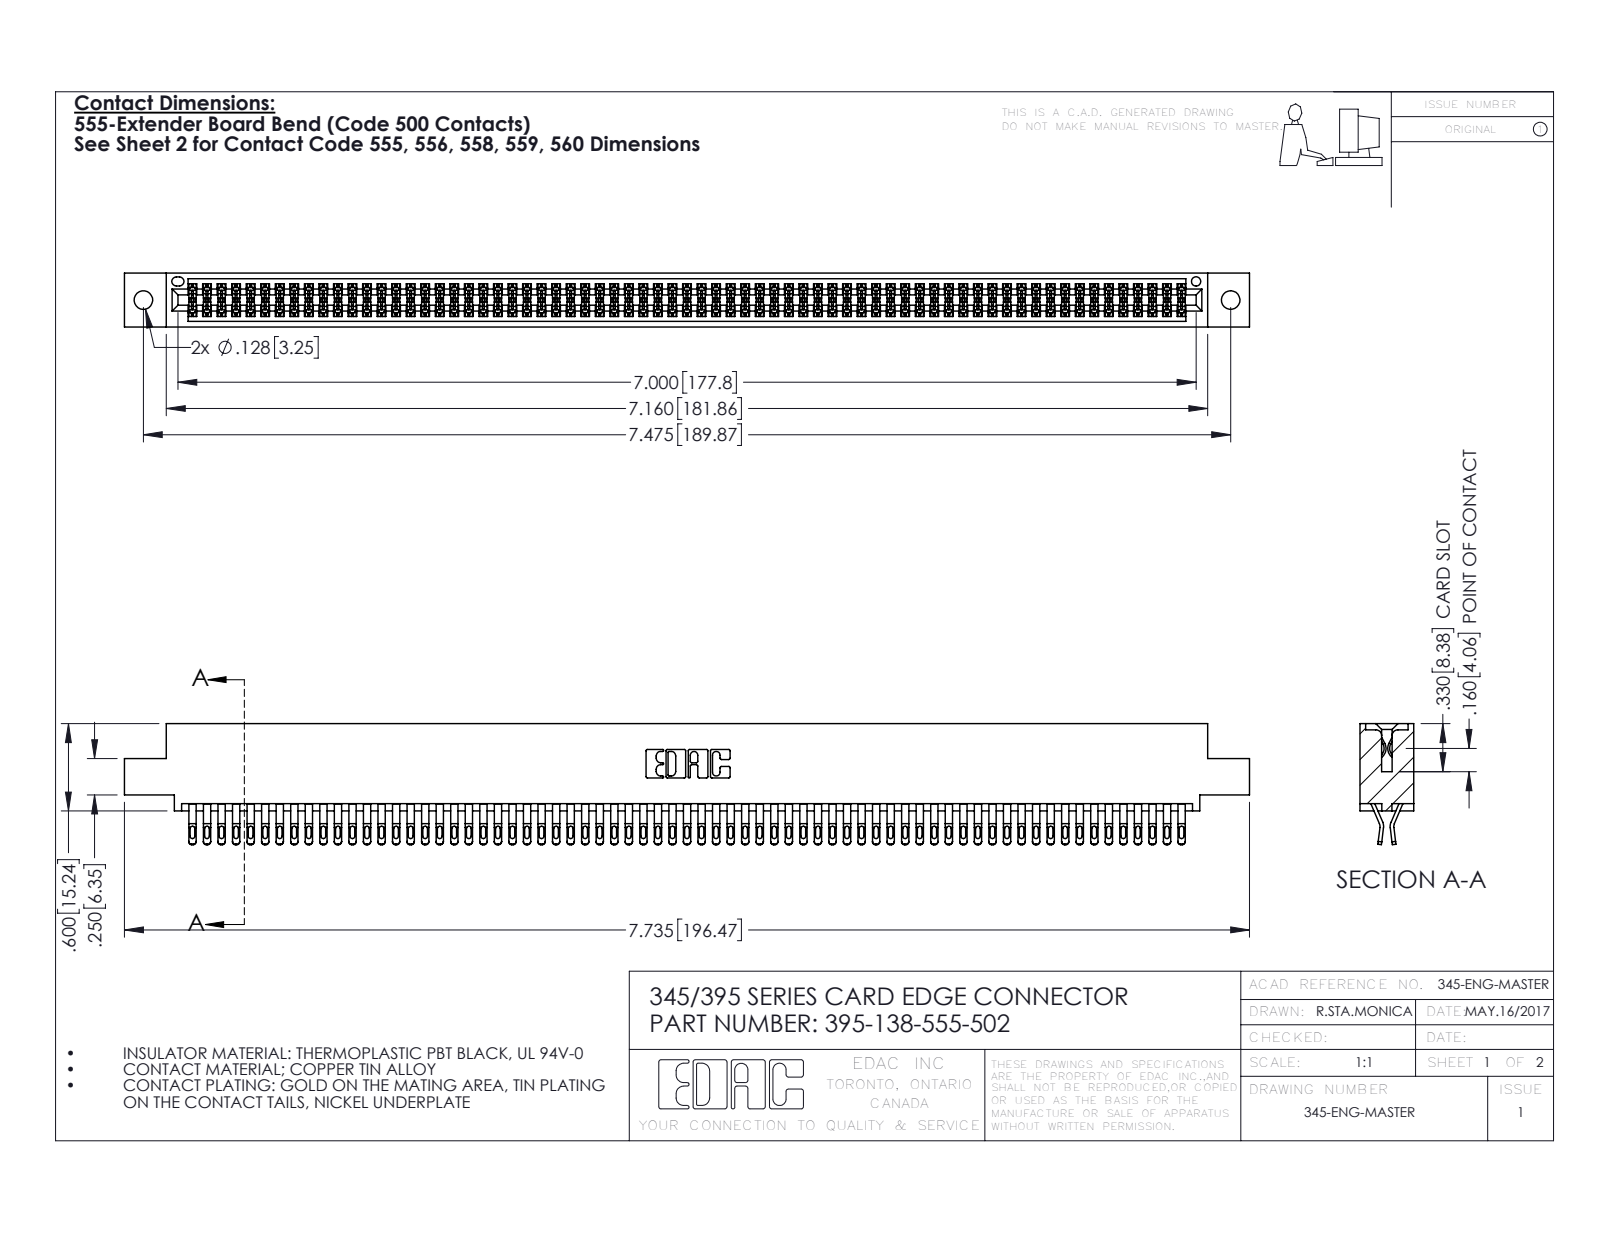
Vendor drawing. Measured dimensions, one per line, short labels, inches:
name: 345-292-001_555 Tail; 345 Part_0.110 Offset - 0.128 Dia; 395-138-555-502
written by: SolidWorks 2016 (CONFIG_CONTROL_DESIGN)
unit: in
bodies: 139 solids, 7858 faces (4362 planar, 3496 cylindrical, 0 other)
size: 7.735 × 0.832 × 0.37
volume: 1.198 in³; area: 47.66 in²
holes: 2× ⌀0.128, 1× ⌀0.064
rounds: 345× R0.016, 276× R0.02, 207× R0.006, 22× R0.01, 6× R0.007, 6× R0.031, 3× R0.026, 2× R0.01
face distances: 0.298, 0.072, 0.025, 0.37, 0.2, 0.098, 0.272, 0.225, 0.175, 0.149
hole spacings: 0.27, 7.239, 7.475
